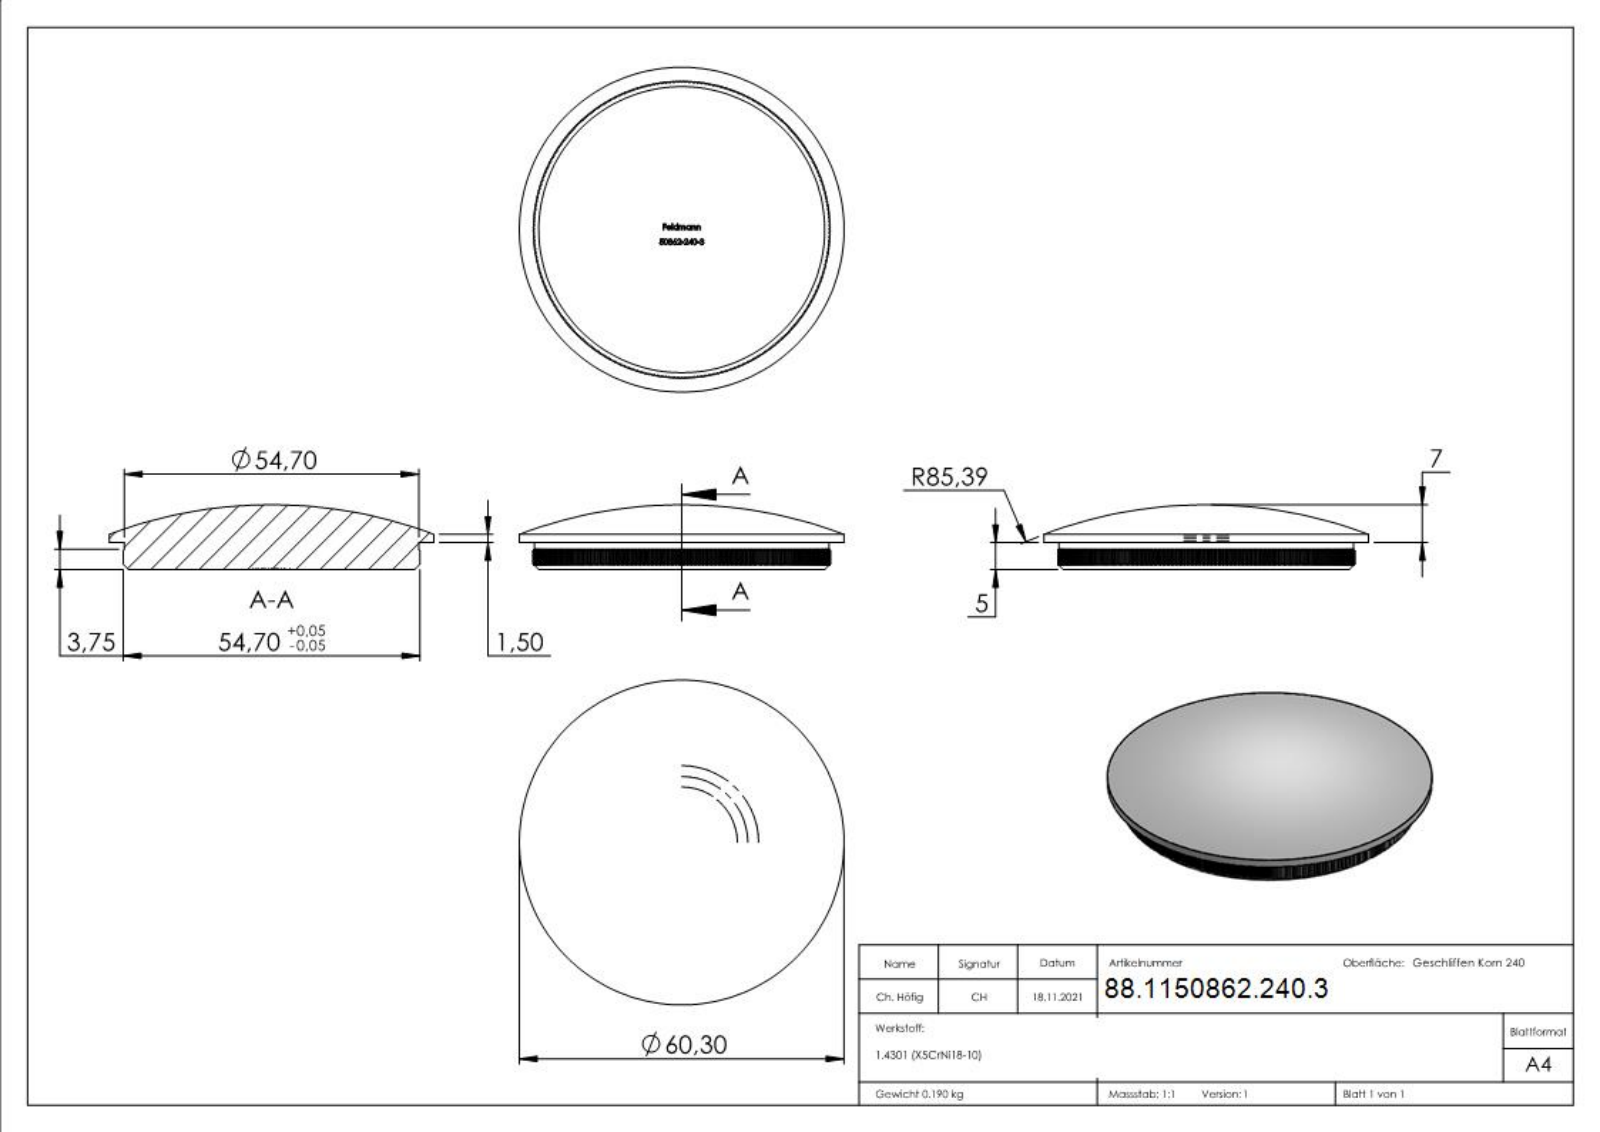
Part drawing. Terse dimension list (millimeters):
name: 50862-240-3
written by: SolidWorks 2018 (CONFIG_CONTROL_DESIGN)
unit: mm
bodies: 1 solid, 1899 faces (949 planar, 412 cylindrical, 538 other)
size: 60.3 × 60.3 × 12
volume: 23 989 mm³; area: 7 161 mm²
bosses: 1× ⌀60.3, 1× ⌀54.7
rounds: 1× R27.55
face distances: 5, 27.34, 27.36, 27.32, 27.38, 4.9, 2.75, 0.31, 2.47, 1.01
